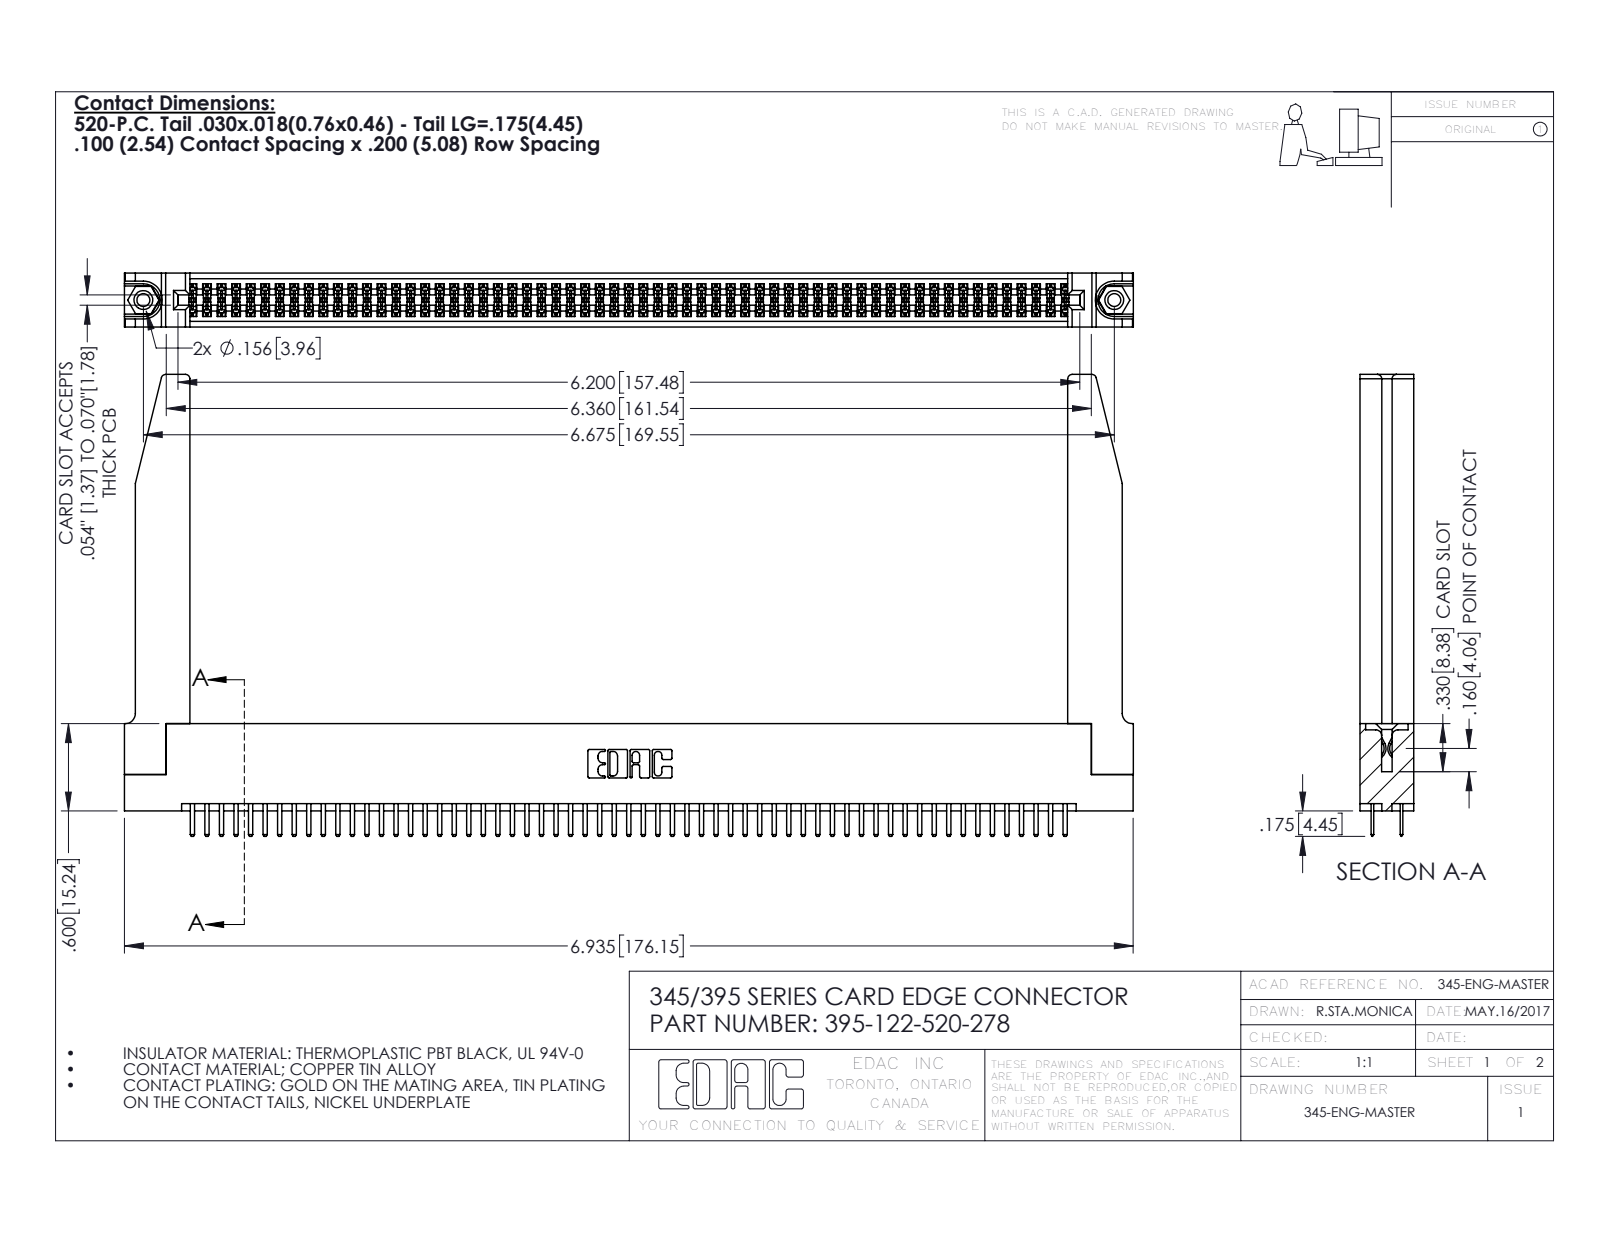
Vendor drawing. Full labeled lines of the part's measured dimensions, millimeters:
Part name (STEP PRODUCT): 345 Part_Flush Mounting Lugs - 0.156 Dia-TH; 345-250-001_345-250-001-102; 345-220-078_345-220-078; 345-292-001_345-293-120 (+1 more)
STEP written by: SolidWorks 2016 (CONFIG_CONTROL_DESIGN)
Units: millimetres
Bodies: 127 solids, 6948 faces (4492 planar, 2404 cylindrical, 52 other)
Overall size (bounding box): 176.2 × 80.6 × 9.4
Volume: 25 010 mm³ · Surface area: 32 570 mm²
Round holes (diameter × count): ⌀2.3 ×2, ⌀3.2 ×2, ⌀4 ×2, ⌀1.6 ×1
Round bosses / shafts (diameter × count): ⌀3.9 ×2
Partial cylindrical surfaces — rounded edges, fillets, slot ends (radius × count): R0.2 ×183, R0.3 ×126, R0.3 ×22, R0.8 ×8, R0.2 ×6, R0.8 ×6, R0.7 ×3, R0.4 ×2
Main face-to-face distances: 1.8, 9.4, 7.6, 5.1, 2.5, 6.9, 0.6, 5.7, 0.6, 1.8
Hole centre spacings: 6.9, 163.6, 169.5
